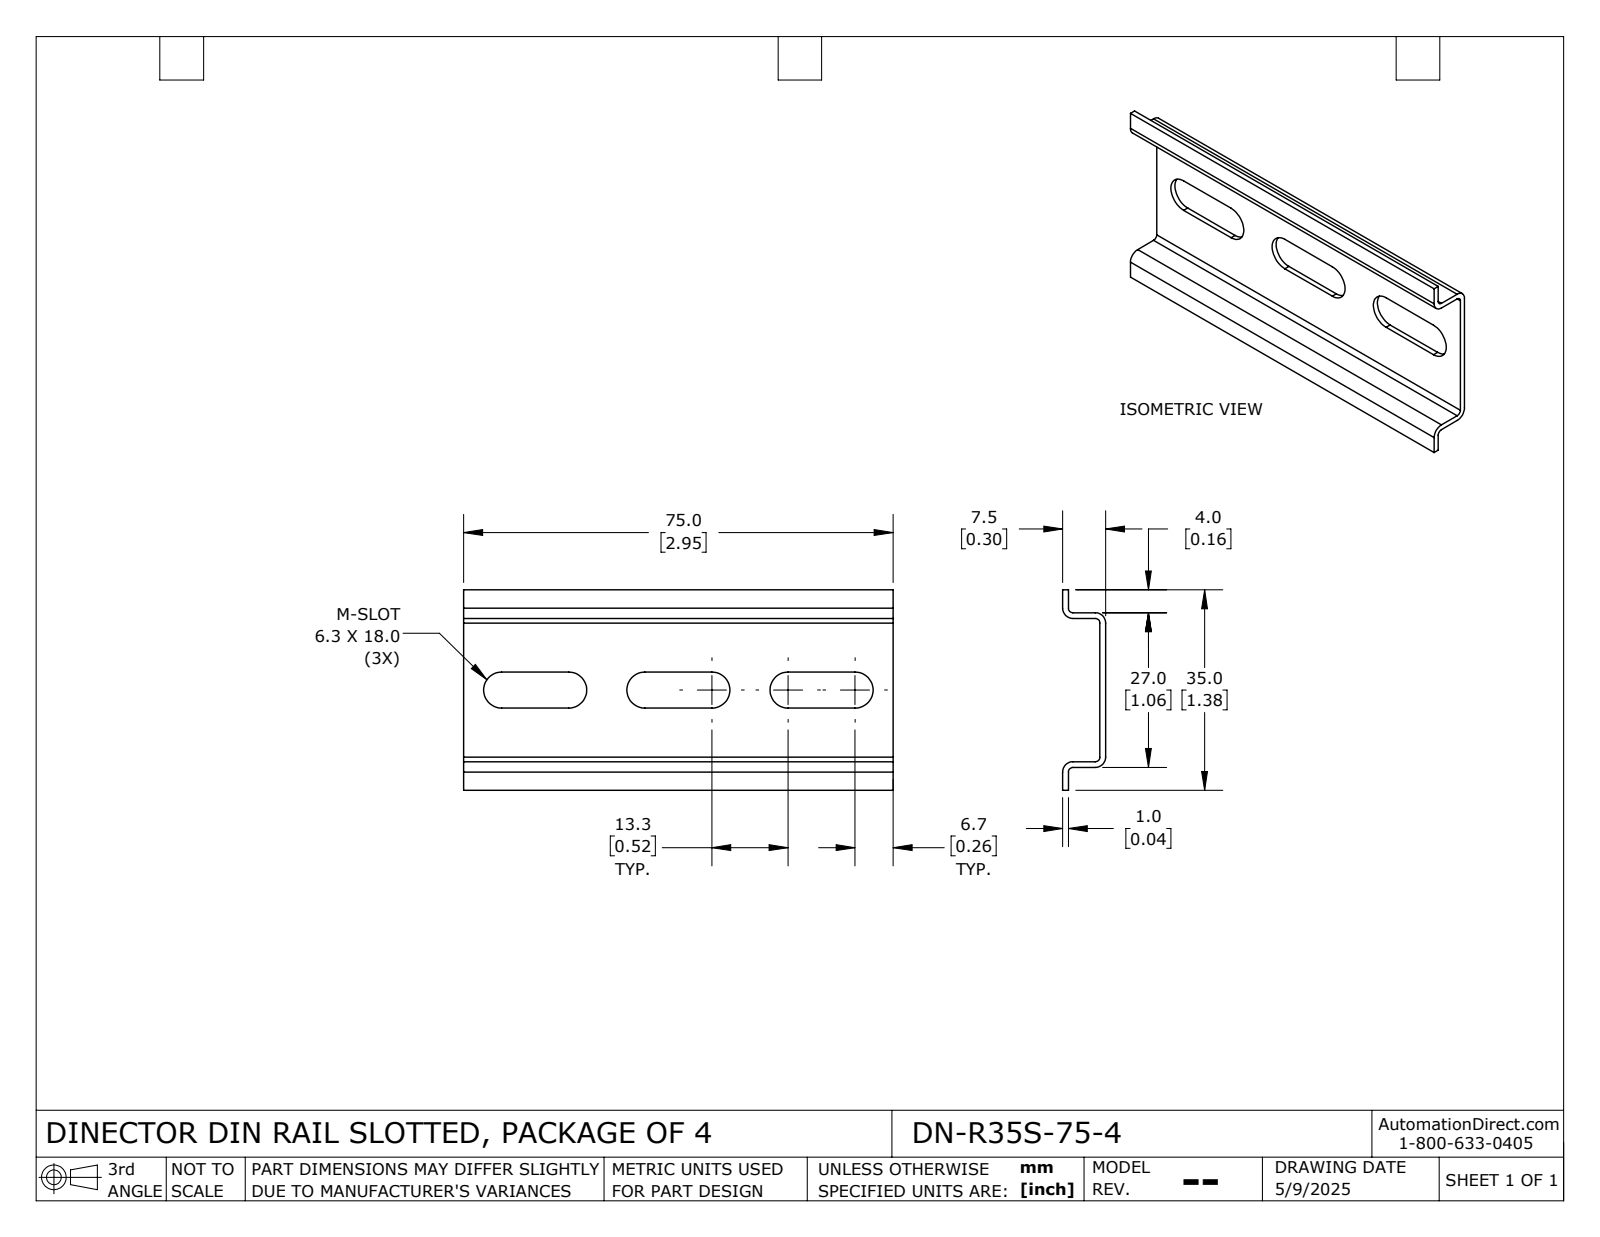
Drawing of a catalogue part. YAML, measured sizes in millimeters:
part_name: "DN-R35S-75-4_Default"
step_written_by: "SolidWorks 2024 (CONFIG_CONTROL_DESIGN)"
units: millimeters
bodies: {solids: 1, faces: 34, planar: 20, cylindrical: 14, other: 0}
overall_size: [75, 35, 7.5]
volume: 3118
surface_area: 6607
partial_cylinders:
  - {radius: 3.15, count: 6}
  - {radius: 0.8, count: 4}
  - {radius: 1.8, count: 4}
face_to_face_distances: [1, 6.5, 26, 7.5, 5.5, 27, 25, 4, 5, 30]
